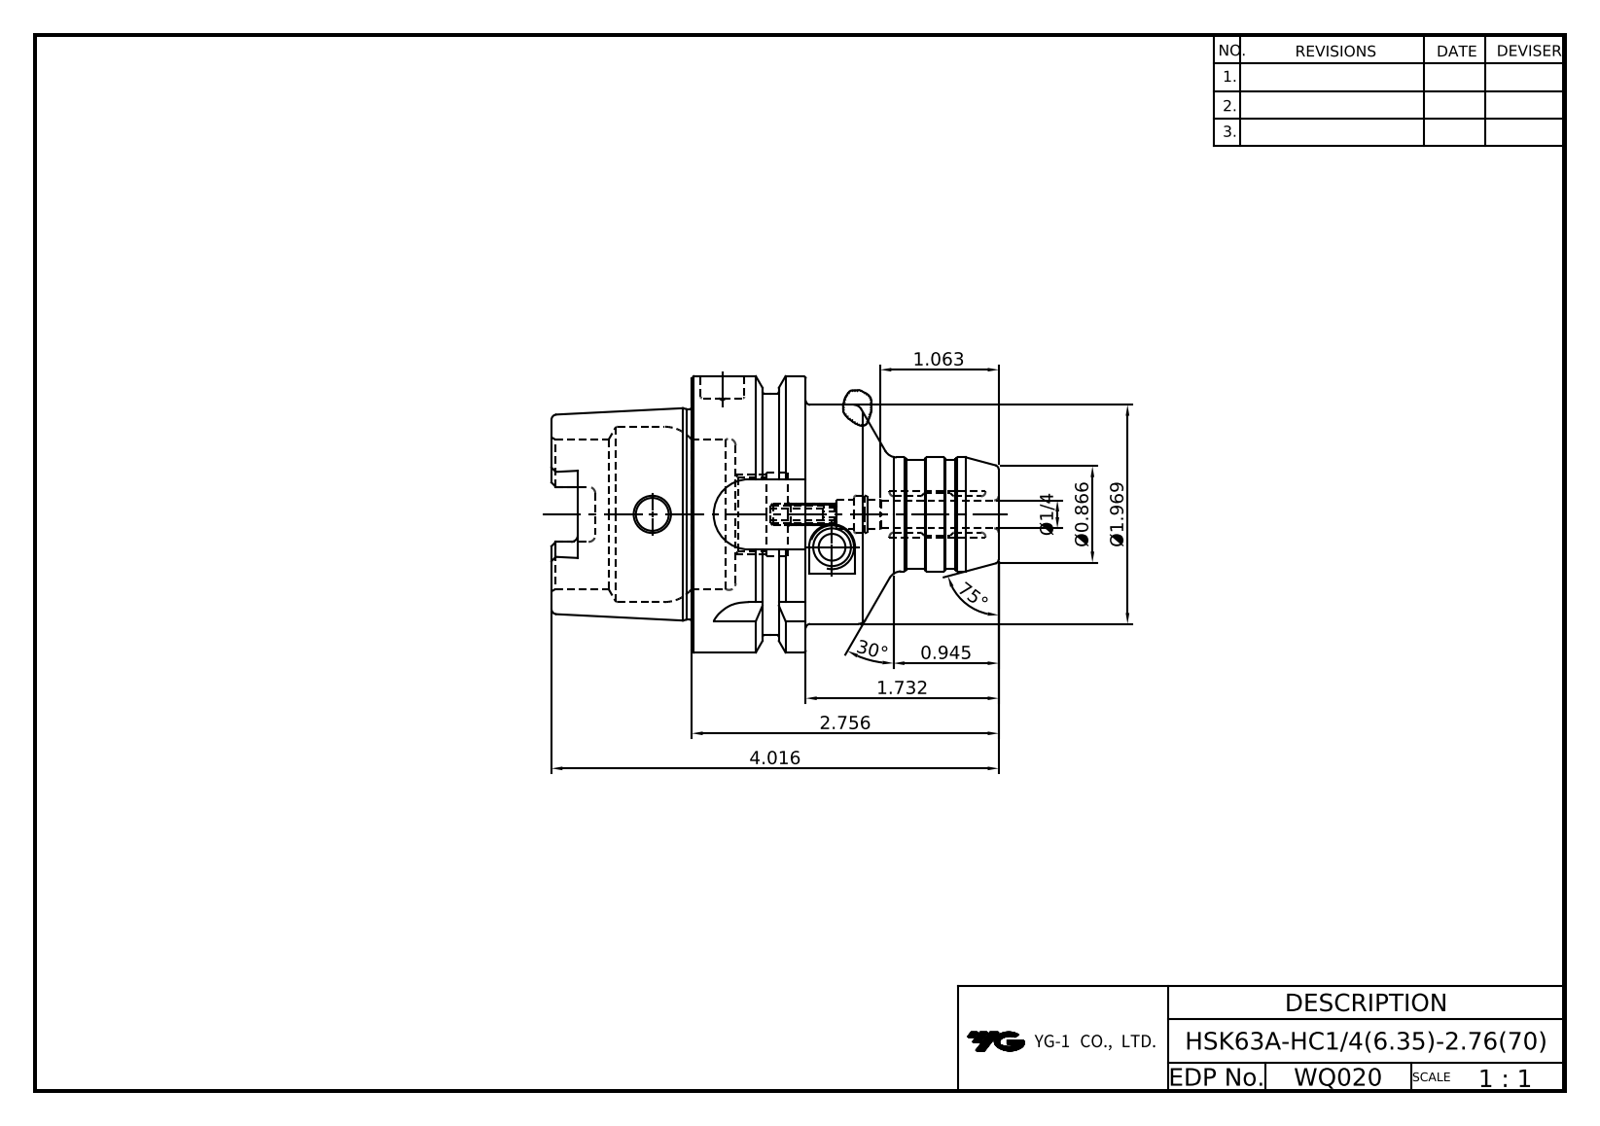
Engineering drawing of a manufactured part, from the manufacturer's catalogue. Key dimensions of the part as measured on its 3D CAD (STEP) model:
Part name (STEP PRODUCT): HSK63A-HC6_35-70
STEP written by: CREO PARAMETRIC BY PTC INC, 2018500 (CONFIG_CONTROL_DESIGN)
Units: millimetres
Bodies: 1 solid, 205 faces (56 planar, 59 cylindrical, 90 other)
Overall size (bounding box): 102 × 63 × 63
Volume: 125 766 mm³ · Surface area: 27 647 mm²
Round holes (diameter × count): ⌀5 ×1, ⌀6.35 ×1, ⌀6.8 ×1, ⌀7.5 ×1, ⌀10 ×1, ⌀17 ×1, ⌀18 ×1, ⌀19 ×1, ⌀34 ×1, ⌀40 ×1
Round bosses / shafts (diameter × count): ⌀63 ×1, ⌀55 ×1, ⌀50 ×1, ⌀48.04 ×1, ⌀26 ×1, ⌀25 ×1
Partial cylindrical surfaces — rounded edges, fillets, slot ends (radius × count): R1.5 ×6, R2.88 ×4, R8 ×4
Main face-to-face distances: 26, 10, 16, 32, 6.12, 9.88, 58, 48, 42, 44
